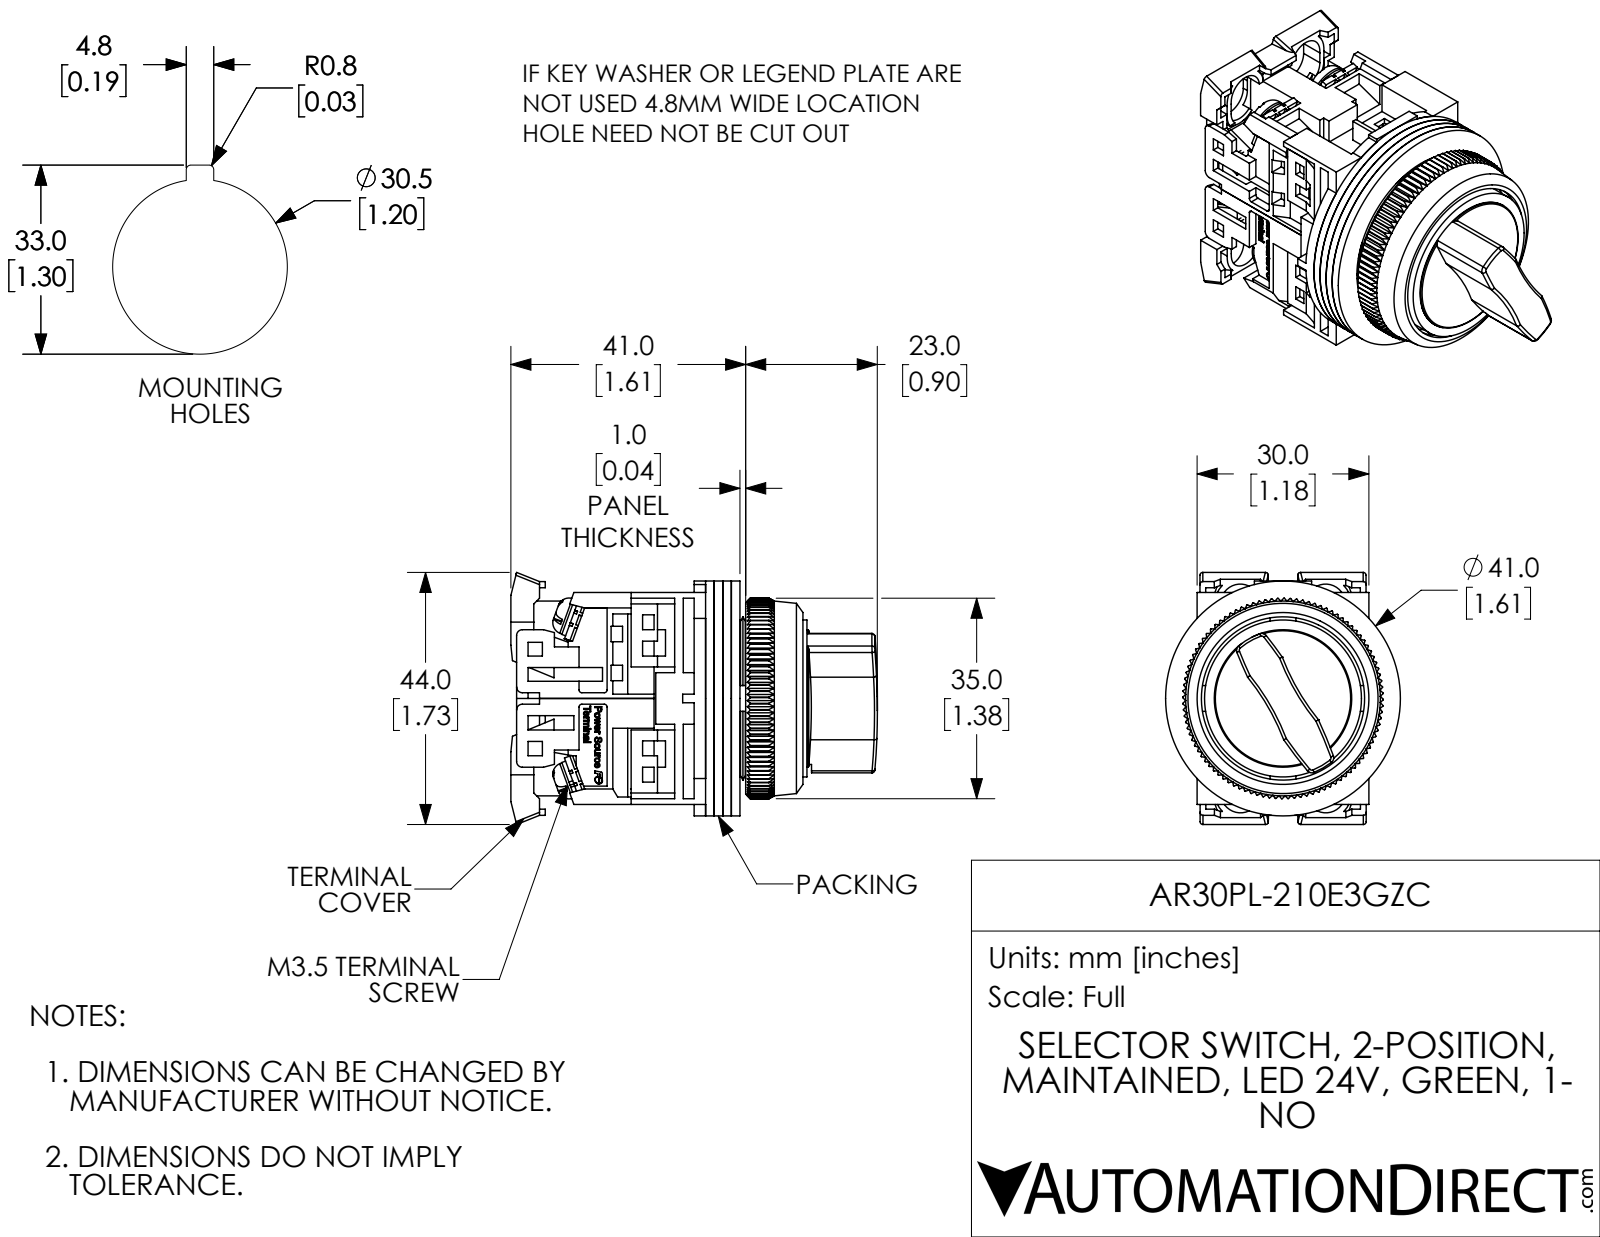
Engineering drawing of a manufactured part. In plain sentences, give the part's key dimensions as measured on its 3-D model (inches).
The part is named "AR30PL-210E3GZC". Its 3-D file was written by "SolidWorks 2017 (AUTOMOTIVE_DESIGN)". It is 25 solids with 2434 faces: 1731 planar, 305 cylindrical and 398 other. Overall it measures 2.52 by 1.732 by 1.614 inches. Its volume is 2.238 cubic inches and its surface area 59.31 square inches. Round holes: 8 of diameter 0.138, 4 of diameter 0.142, 1 of diameter 0.118, 1 of diameter 0.472, 1 of diameter 0.709, 1 of diameter 0.768, 1 of diameter 0.827, 1 of diameter 1.122, 1 of diameter 1.181, 1 of diameter 1.252. Round bosses or shafts: 4 of diameter 0.26, 4 of diameter 0.138, 2 of diameter 0.063, 1 of diameter 1.614, 1 of diameter 1.15, 1 of diameter 1.079, 1 of diameter 0.945, 1 of diameter 0.886. Partial cylindrical surfaces (rounded edges, fillets, slot ends): 16 of radius 0.059, 12 of radius 0.02, 8 of radius 0.039, 4 of radius 0.138, 4 of radius 0.177, 2 of radius 0.118, 2 of radius 1.575, 2 of radius 2.953. The main face-to-face distances are 0.059, 0.118, 0.177, 0.039, 0.079, 1.417, 1.358, 0.811, 0.197, 0.02. The hole center spacings are 0.579, 0.61.
